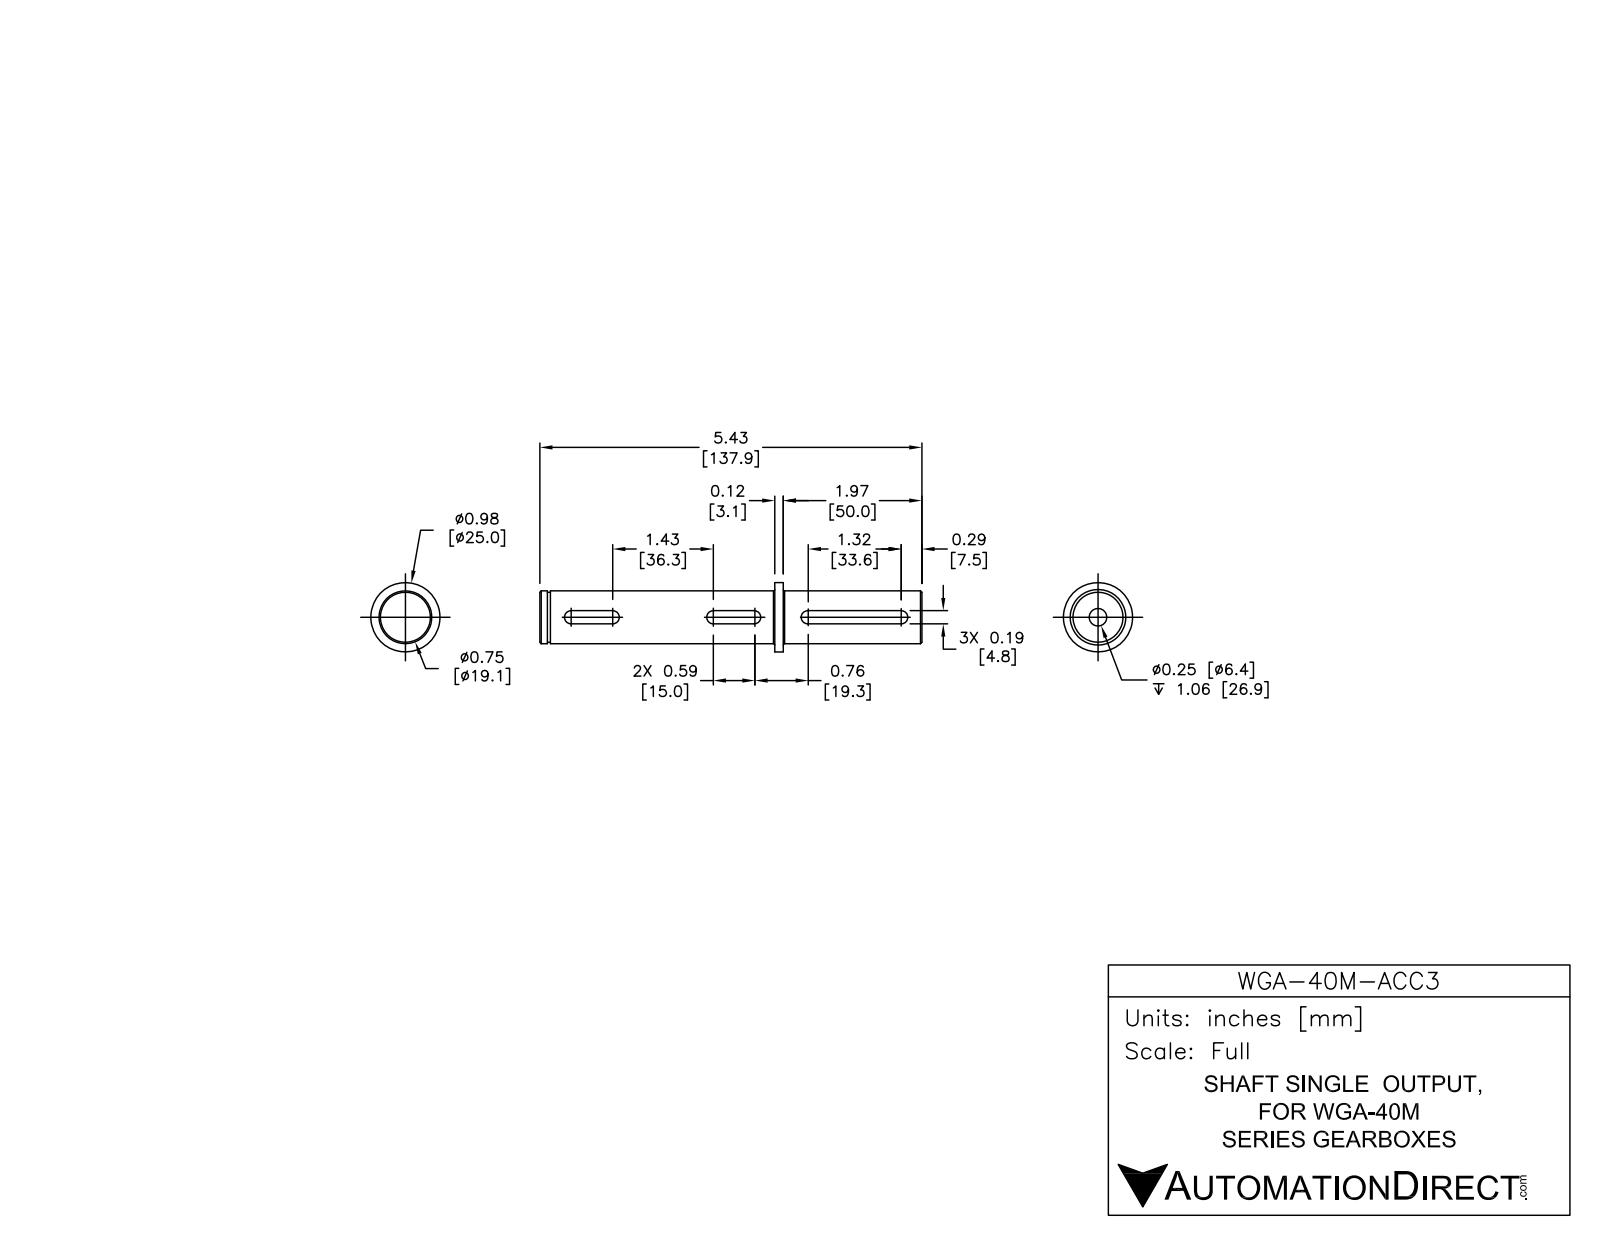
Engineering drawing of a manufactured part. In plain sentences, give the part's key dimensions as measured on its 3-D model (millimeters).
The part is named "WGA-40M-ACC3". Its 3-D file was written by "SolidWorks 2014 (AUTOMOTIVE_DESIGN)". It is 1 solid with 48 faces: 16 planar, 20 cylindrical and 12 other. Overall it measures 137.9 by 25 by 25 millimeters. Its volume is 38 480 cubic millimeters and its surface area 10 010 square millimeters. Round holes: 1 of diameter 5.1, 1 of diameter 6.4. Round bosses or shafts: 1 of diameter 25, 1 of diameter 19.1, 1 of diameter 18. Partial cylindrical surfaces (rounded edges, fillets, slot ends): 5 of radius 2.4, 1 of radius 2.5. The main face-to-face distances are 137.9, 84.8, 53.1, 87.9, 3, 50, 4.7, 3.8, 81, 84.
